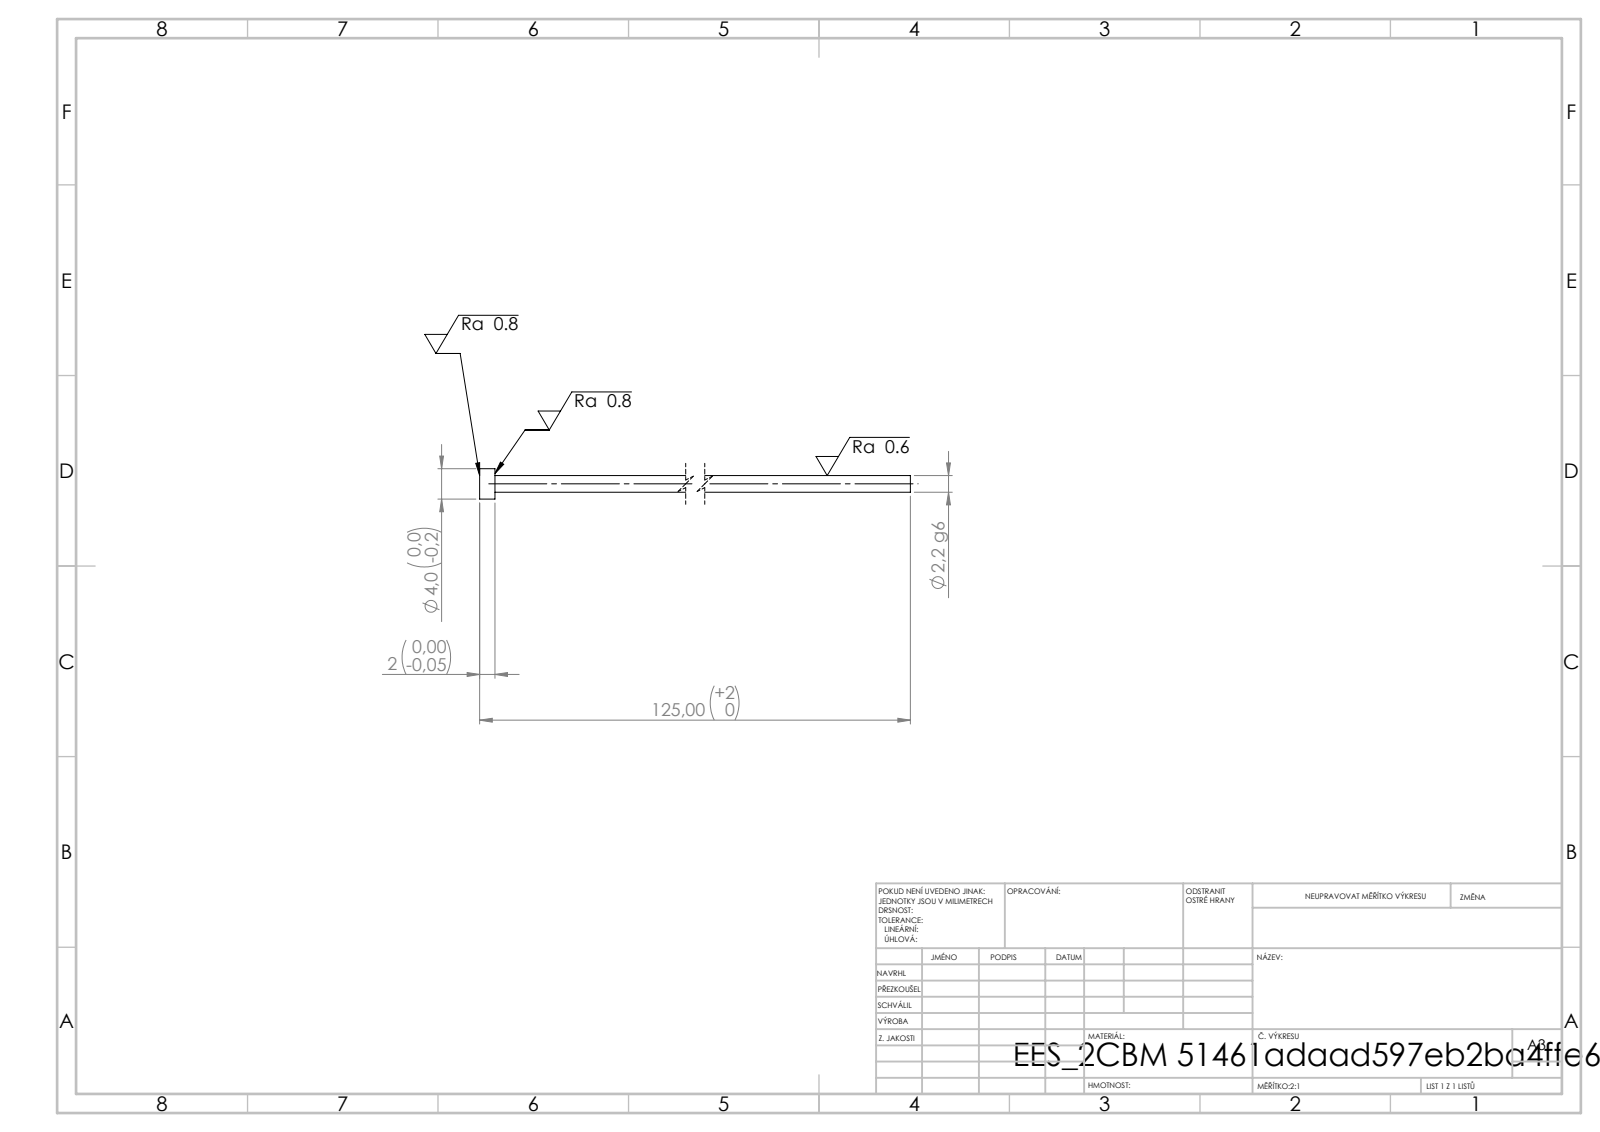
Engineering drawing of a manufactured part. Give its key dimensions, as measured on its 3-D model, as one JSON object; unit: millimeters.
{"step_written_by": "SolidWorks 2019 (CONFIG_CONTROL_DESIGN)", "units": "millimeters", "bodies": {"solids": 1, "faces": 7, "planar": 3, "cylindrical": 4, "other": 0}, "overall_size": [125, 4, 4], "volume_mm3": 493, "surface_area_mm2": 900, "round_bosses_or_shafts": [[4, 1], [2.2, 1]], "face_to_face_distances": [2, 125, 123]}
